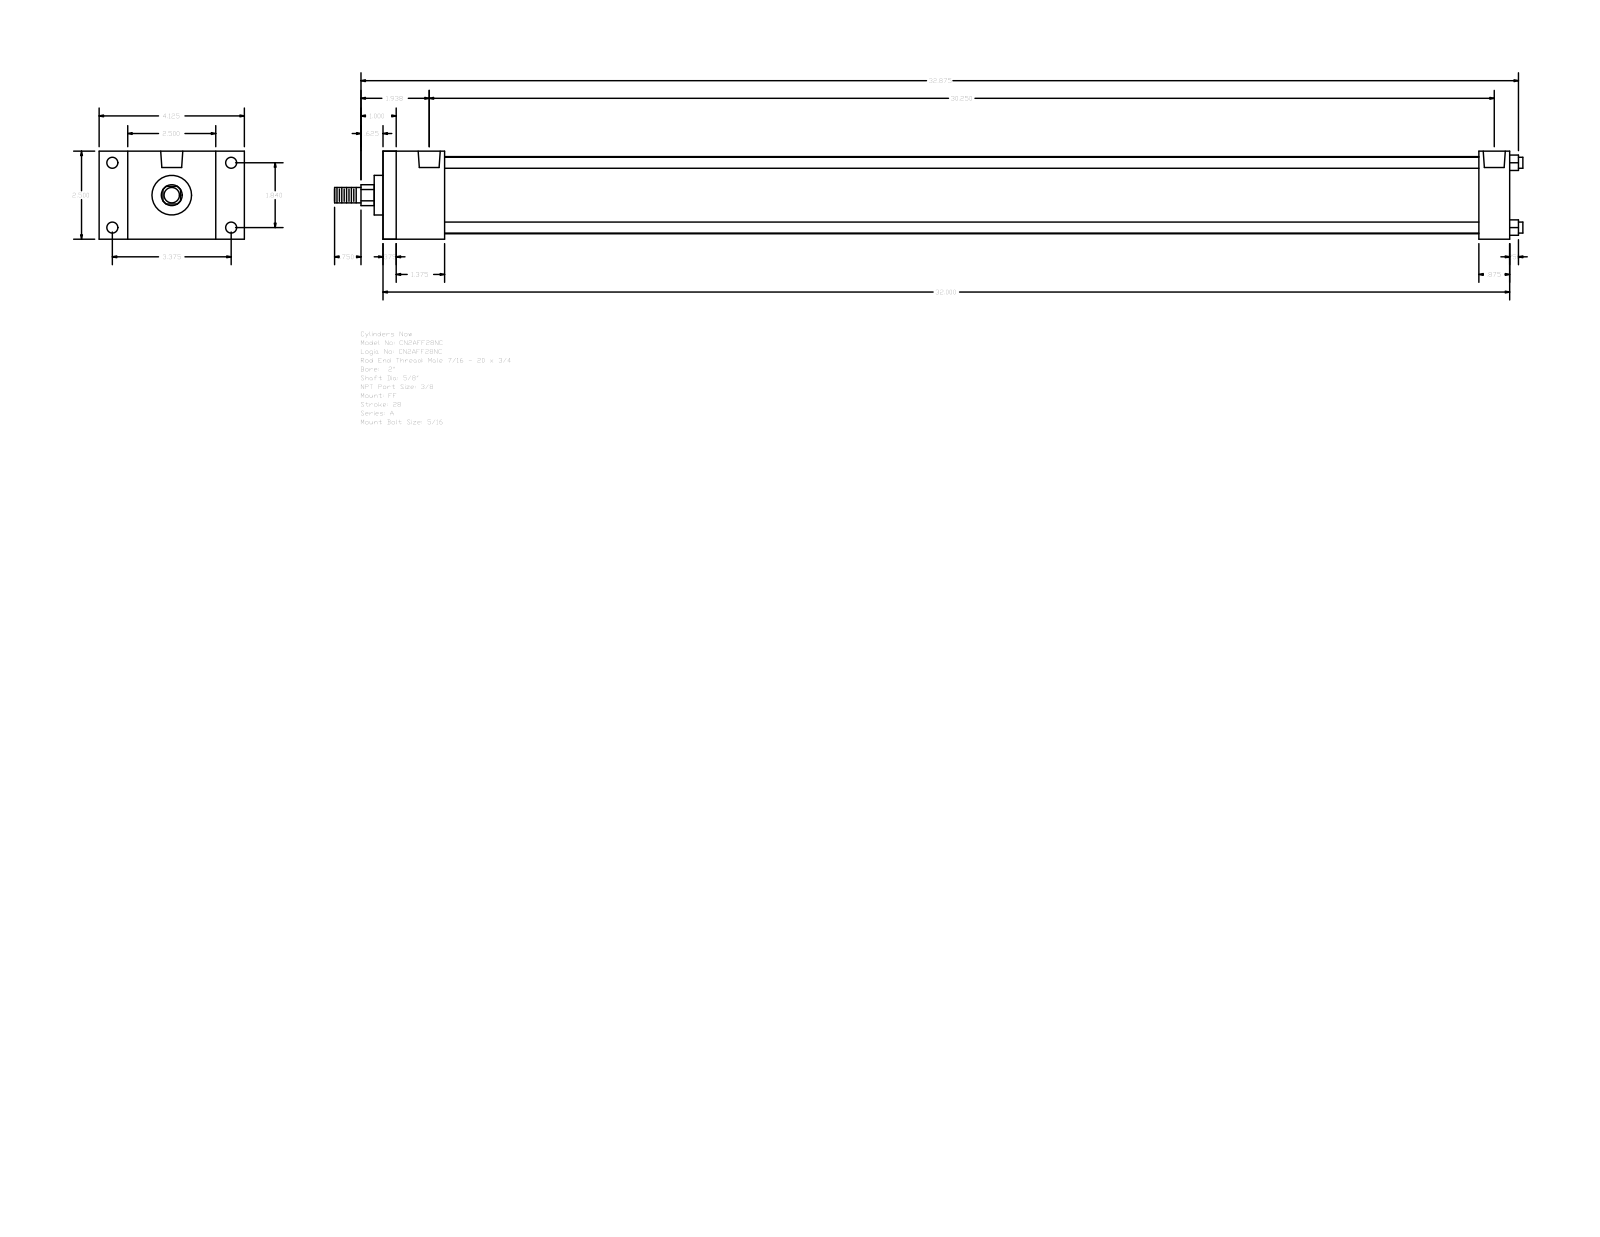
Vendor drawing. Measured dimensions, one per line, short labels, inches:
name: A_FF__0200_0.625
written by: GSSL Pune (CONFIG_CONTROL_DESIGN)
unit: in
bodies: 0 solids, 92 faces (64 planar, 28 cylindrical, 0 other)
size: 33.75 × 4.125 × 2.5
holes: 4× ⌀0.219, 4× ⌀0.313, 2× ⌀0.627
bosses: 4× ⌀0.313, 1× ⌀2.19, 1× ⌀1.125, 1× ⌀0.625, 1× ⌀0.437
rounds: 1× R0.297
face distances: 2.5, 32, 0.375, 31.625, 1.375, 1.75, 31.125, 30.75, 29.375, 30.25
hole spacings: 1.84, 3.375, 3.844, 29.937, 0.156, 0.157, 30.093, 30.094
